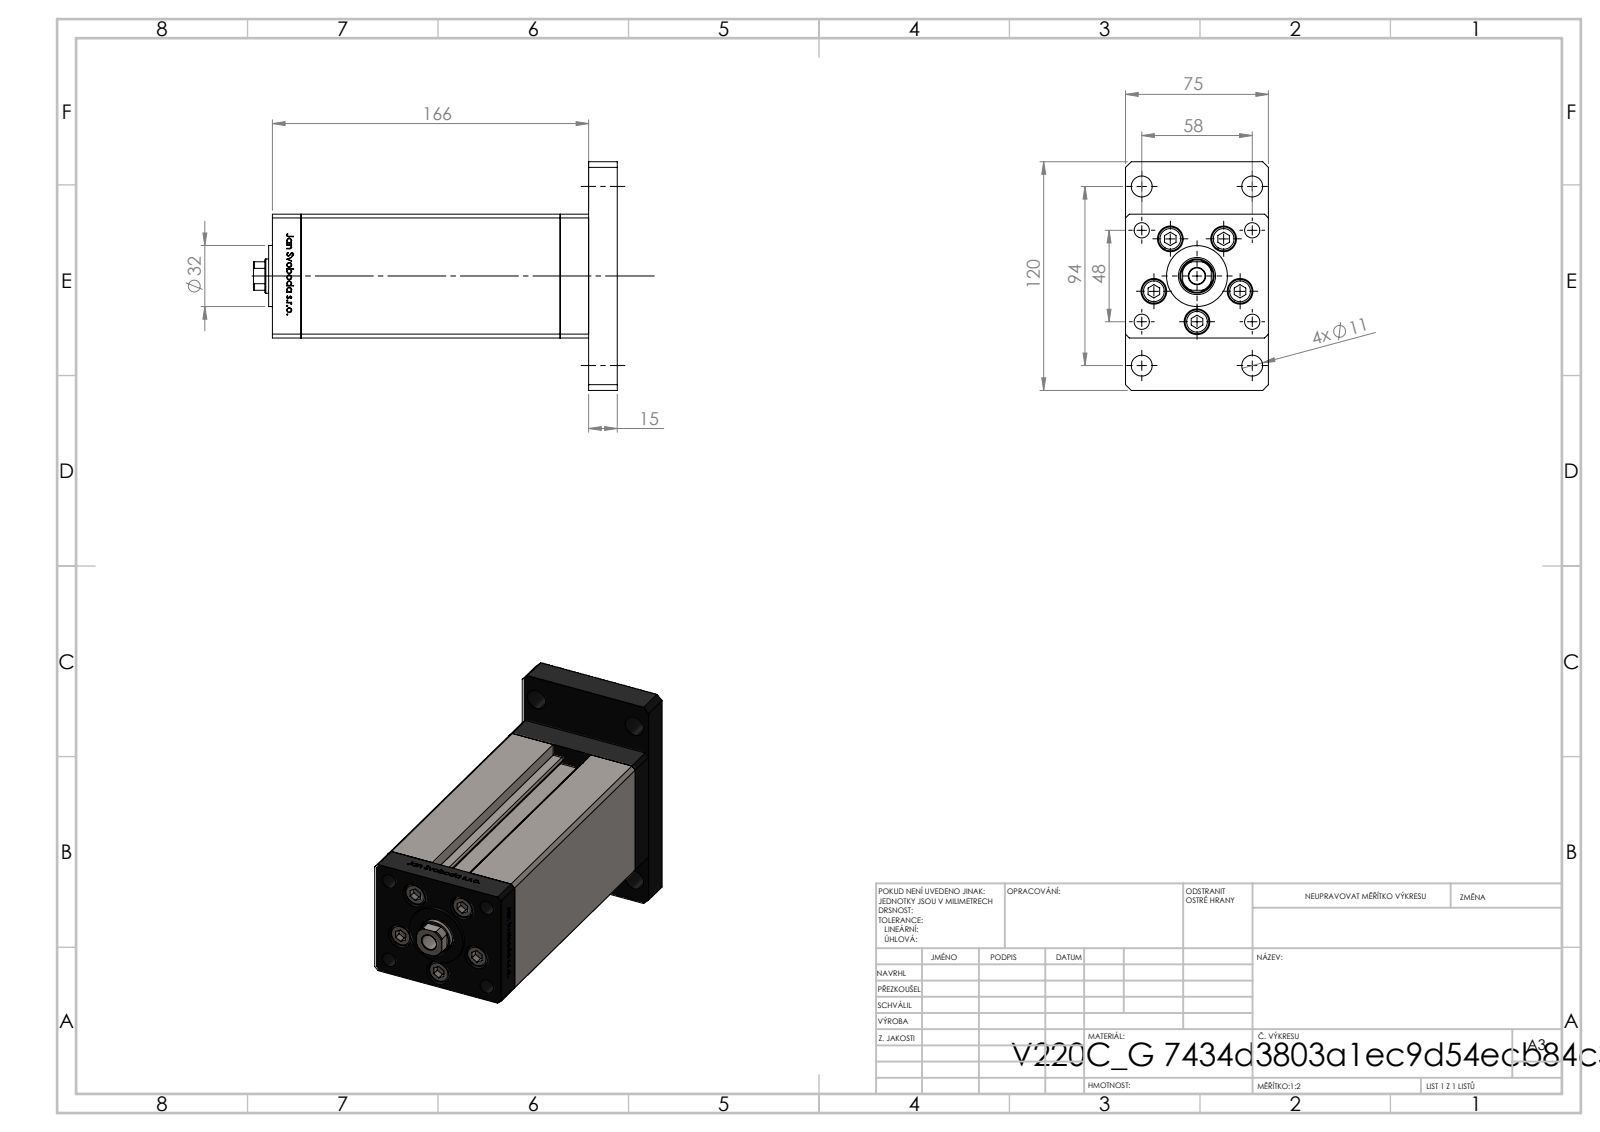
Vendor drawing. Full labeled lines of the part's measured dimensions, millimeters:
Part name (STEP PRODUCT): V220C_VC_G; V220C_G_MIDDLE; V220C_FRONT_G; V220C BACK_G (+2 more)
STEP written by: SolidWorks 2019 (CONFIG_CONTROL_DESIGN)
Units: millimetres
Bodies: 19 solids, 1311 faces (516 planar, 189 cylindrical, 606 other)
Overall size (bounding box): 191 × 120 × 75
Volume: 842 873 mm³ · Surface area: 158 994 mm²
Round holes (diameter × count): ⌀8 ×9, ⌀9 ×5, ⌀13.5 ×5, ⌀11 ×4, ⌀12.5 ×4, ⌀2 ×2, ⌀13.16 ×2, ⌀8.5 ×1, ⌀18 ×1, ⌀19.5 ×1, ⌀48 ×1
Round bosses / shafts (diameter × count): ⌀12.5 ×5, ⌀32 ×1
Partial cylindrical surfaces — rounded edges, fillets, slot ends (radius × count): R0.93 ×2, R8.5 ×1
Main face-to-face distances: 15, 75, 151, 166, 65, 136, 30, 13, 28, 181
Hole centre spacings: 24, 23, 37.64, 55.23, 58, 62.39, 71, 91.68
